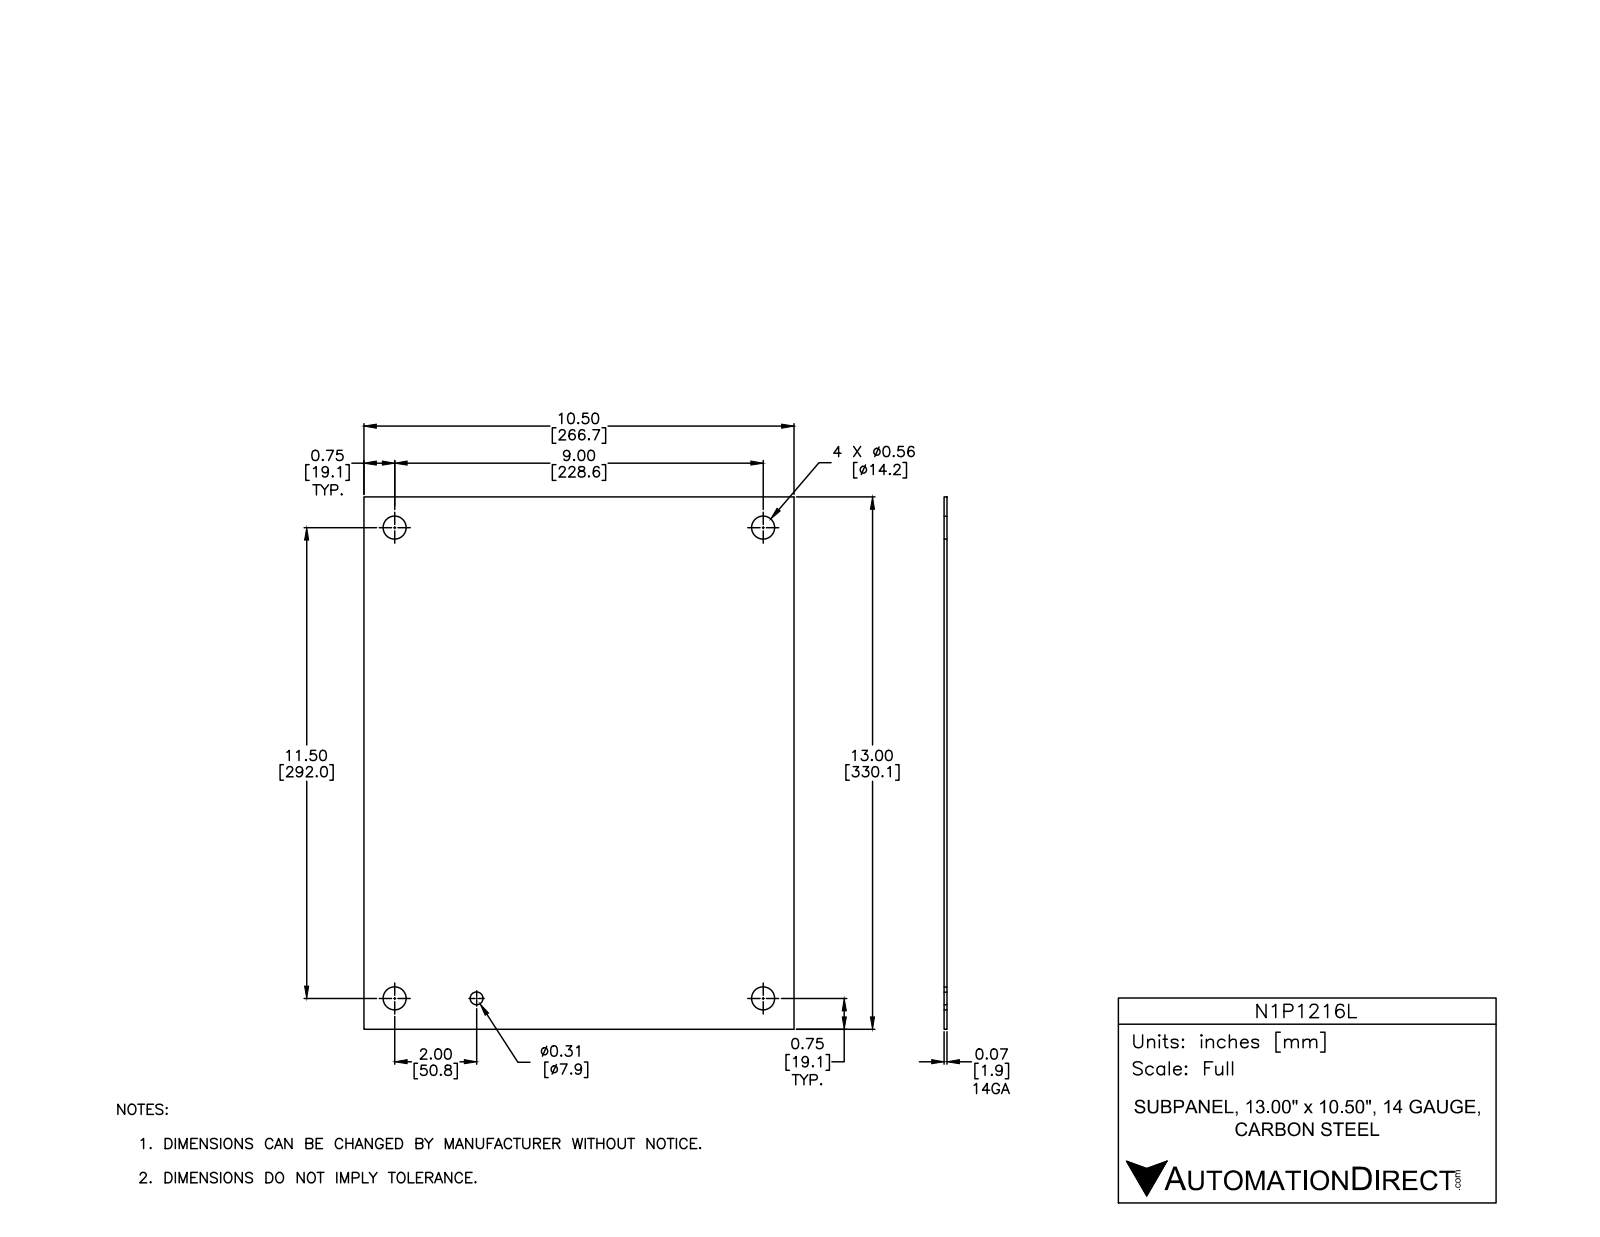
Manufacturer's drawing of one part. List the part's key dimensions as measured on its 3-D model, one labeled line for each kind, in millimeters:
Part name (STEP PRODUCT): N1P1216L-1
STEP written by: Autodesk Inventor 2012 (AUTOMOTIVE_DESIGN)
Units: millimetres
Bodies: 1 solid, 11 faces (6 planar, 5 cylindrical, 0 other)
Overall size (bounding box): 330.2 × 266.7 × 1.9
Volume: 164 200 mm³ · Surface area: 177 400 mm²
Round holes (diameter × count): ⌀14.3 ×4, ⌀7.9 ×1
Main face-to-face distances: 1.9, 266.7, 330.2
Hole centre spacings: 228.6, 292.1, 370.9, 50.8, 177.8, 296.5, 342
